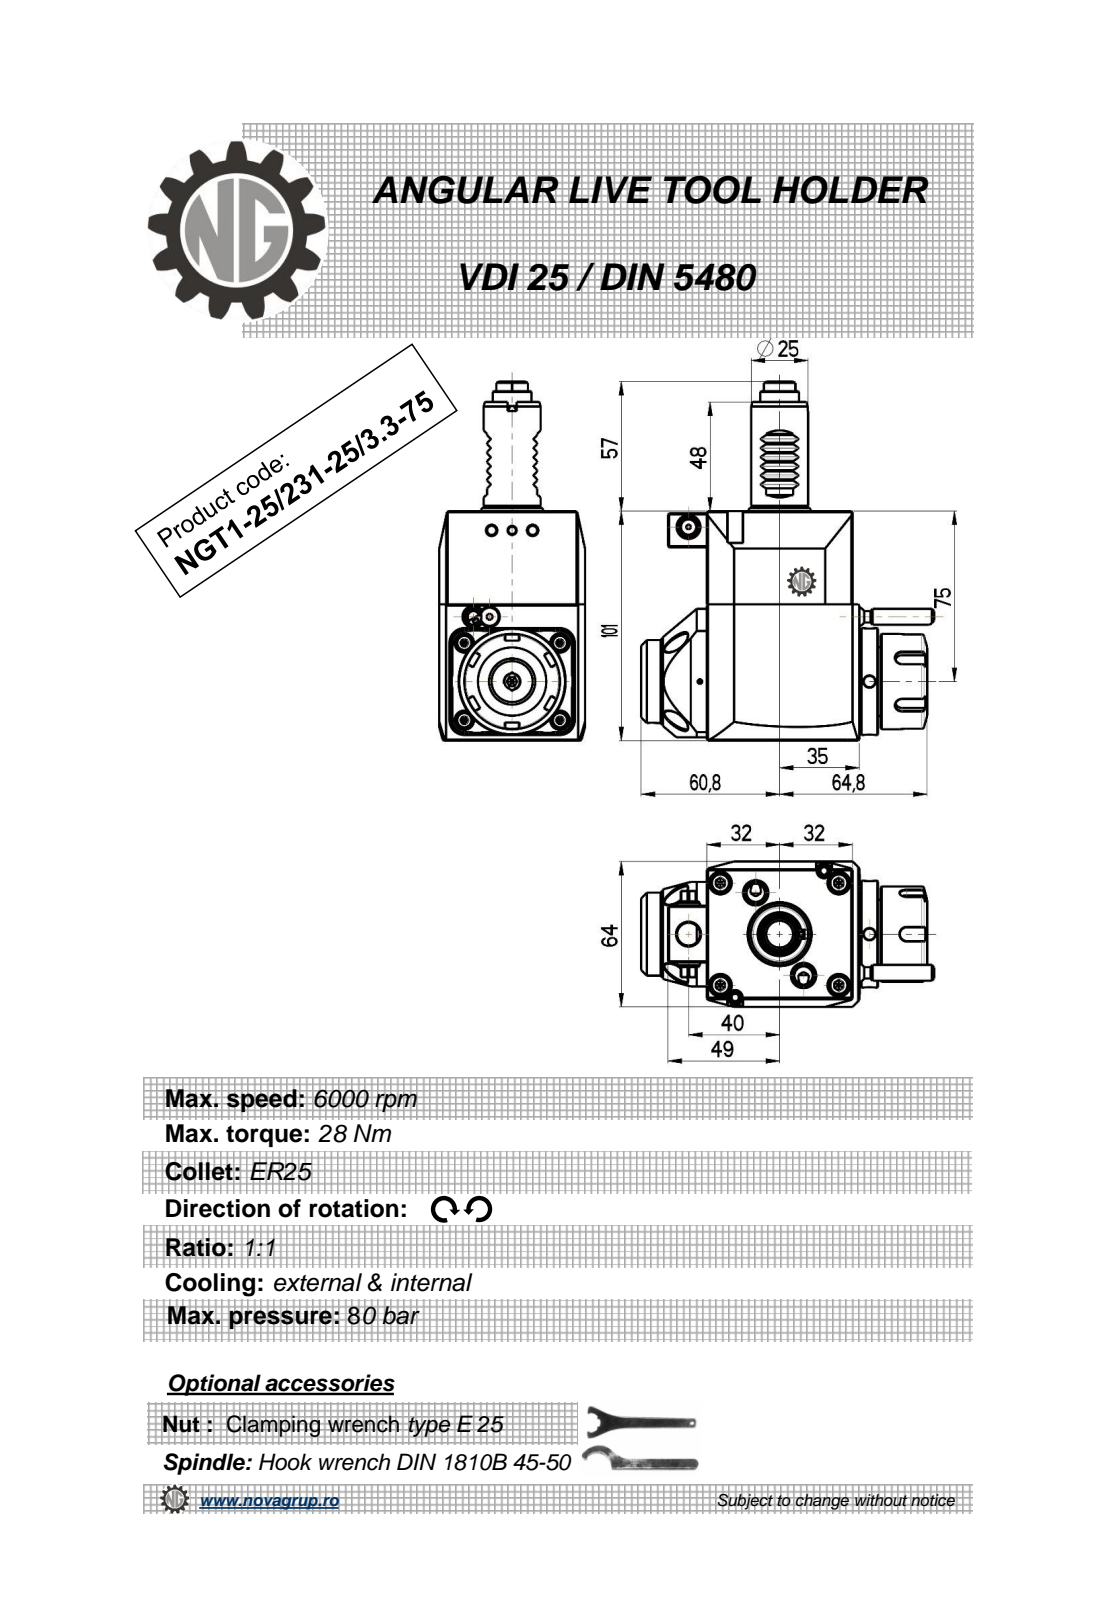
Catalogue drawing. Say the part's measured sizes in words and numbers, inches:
The part is named "NGT1_25_231_25_3_3_75". Its 3-D file was written by "PRO/ENGINEER BY PARAMETRIC TECHNOLOGY CORPORATION, 2010280 (CONFIG_CONTROL_DESIGN)". It is 1 solid with 525 faces: 199 planar, 159 cylindrical and 167 other. Overall it measures 6.22 by 5.064 by 2.52 inches. Its volume is 32.57 cubic inches and its surface area 79.37 square inches. Round holes: 2 of diameter 0.197, 2 of diameter 0.335, 1 of diameter 0.079, 1 of diameter 0.098, 1 of diameter 0.118, 1 of diameter 0.394, 1 of diameter 0.799. Round bosses or shafts: 2 of diameter 0.313, 1 of diameter 1.85, 1 of diameter 1.654, 1 of diameter 1.437, 1 of diameter 1.433, 1 of diameter 1.299, 1 of diameter 0.984, 1 of diameter 0.669. Partial cylindrical surfaces (rounded edges, fillets, slot ends): 32 of radius 0.075, 12 of radius 0.012, 5 of radius 0.118, 1 of radius 0.152, 1 of radius 0.239, 1 of radius 0.272, 1 of radius 0.413, 1 of radius 1.26. The main face-to-face distances are 2.52, 3.976, 0.126, 2.646, 0.315, 0.118, 2.638, 2.961, 0.441, 0.323. The hole center spacings are 1.307, 1.639, 2.618, 3.128, 4.117.
